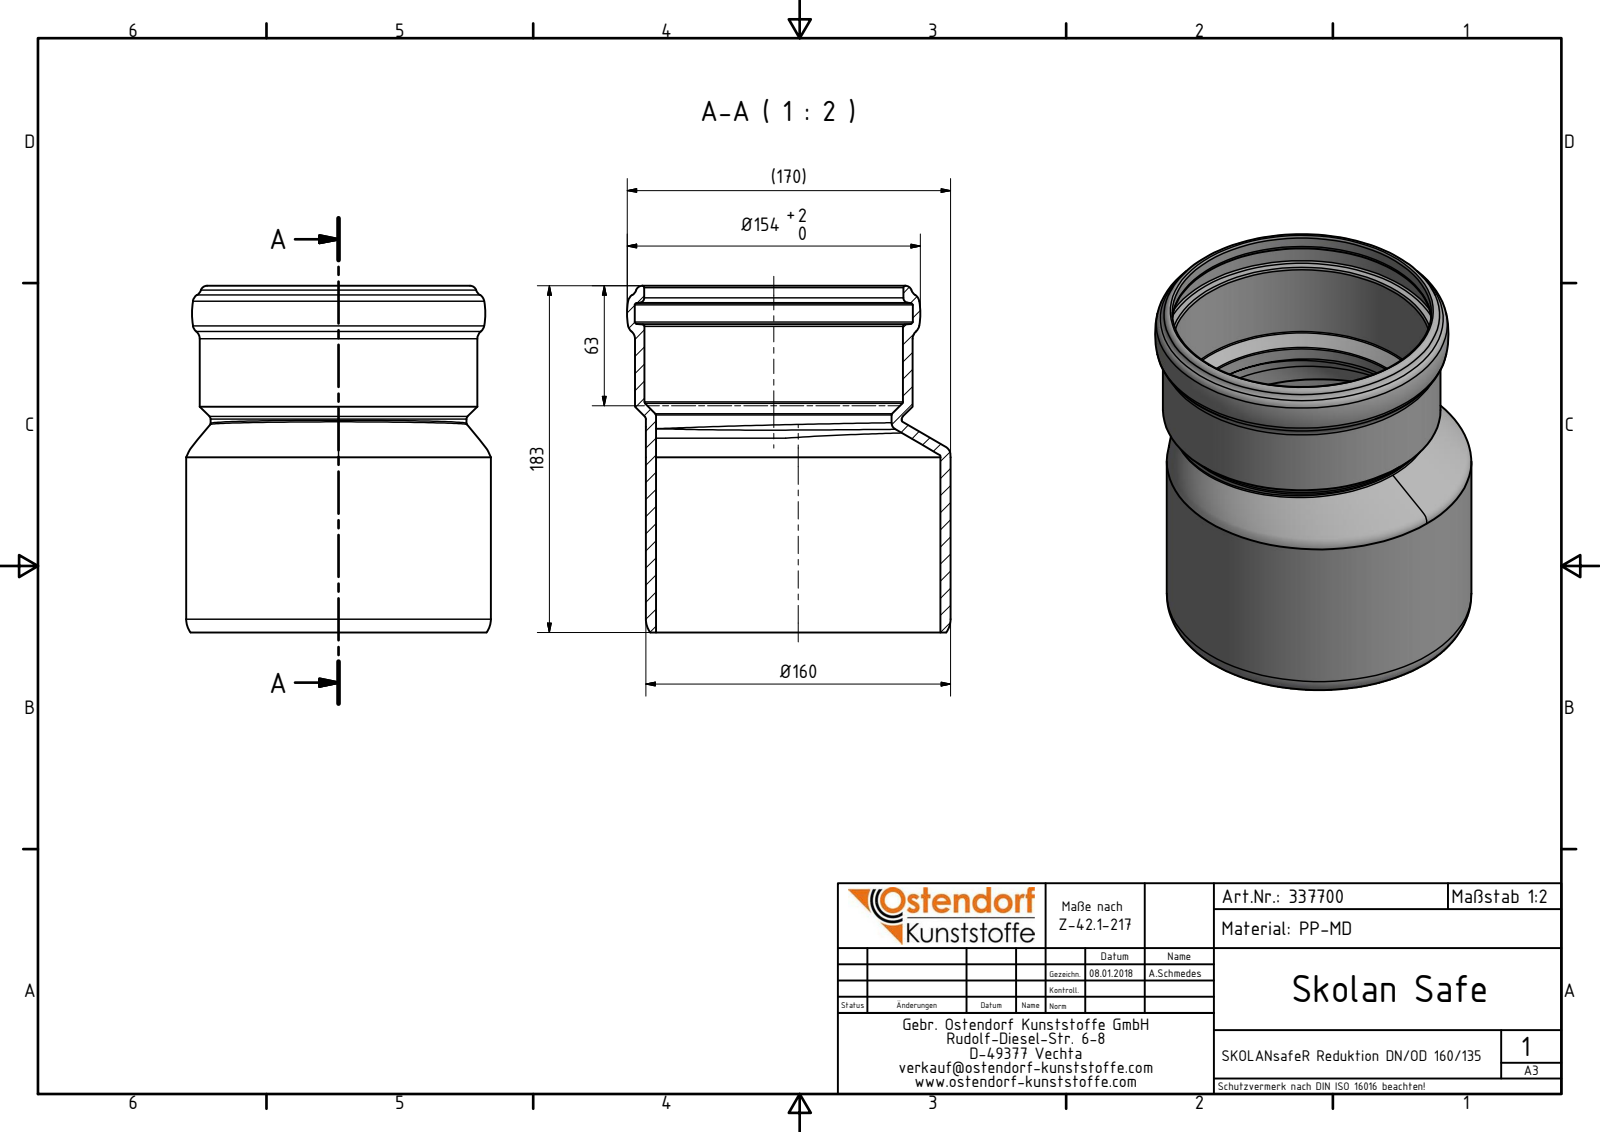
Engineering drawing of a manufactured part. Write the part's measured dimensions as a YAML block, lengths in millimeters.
part_name: "337700 SKOLANsafeR Reduktion DN_OD 160_135"
step_written_by: "Autodesk Inventor 2016 (AUTOMOTIVE_DESIGN)"
units: millimeters
bodies: {solids: 1, faces: 33, planar: 1, cylindrical: 8, other: 24}
overall_size: [182, 169.85, 160]
volume: 458423
surface_area: 183847
round_holes:
  - {diameter: 123.7, count: 1}
  - {diameter: 135.8, count: 1}
  - {diameter: 136.1, count: 1}
  - {diameter: 146, count: 1}
  - {diameter: 149.4, count: 1}
round_bosses_or_shafts:
  - {diameter: 160, count: 1}
  - {diameter: 145.8, count: 1}
  - {diameter: 134.3, count: 1}
hole_center_spacings: [12.85]
